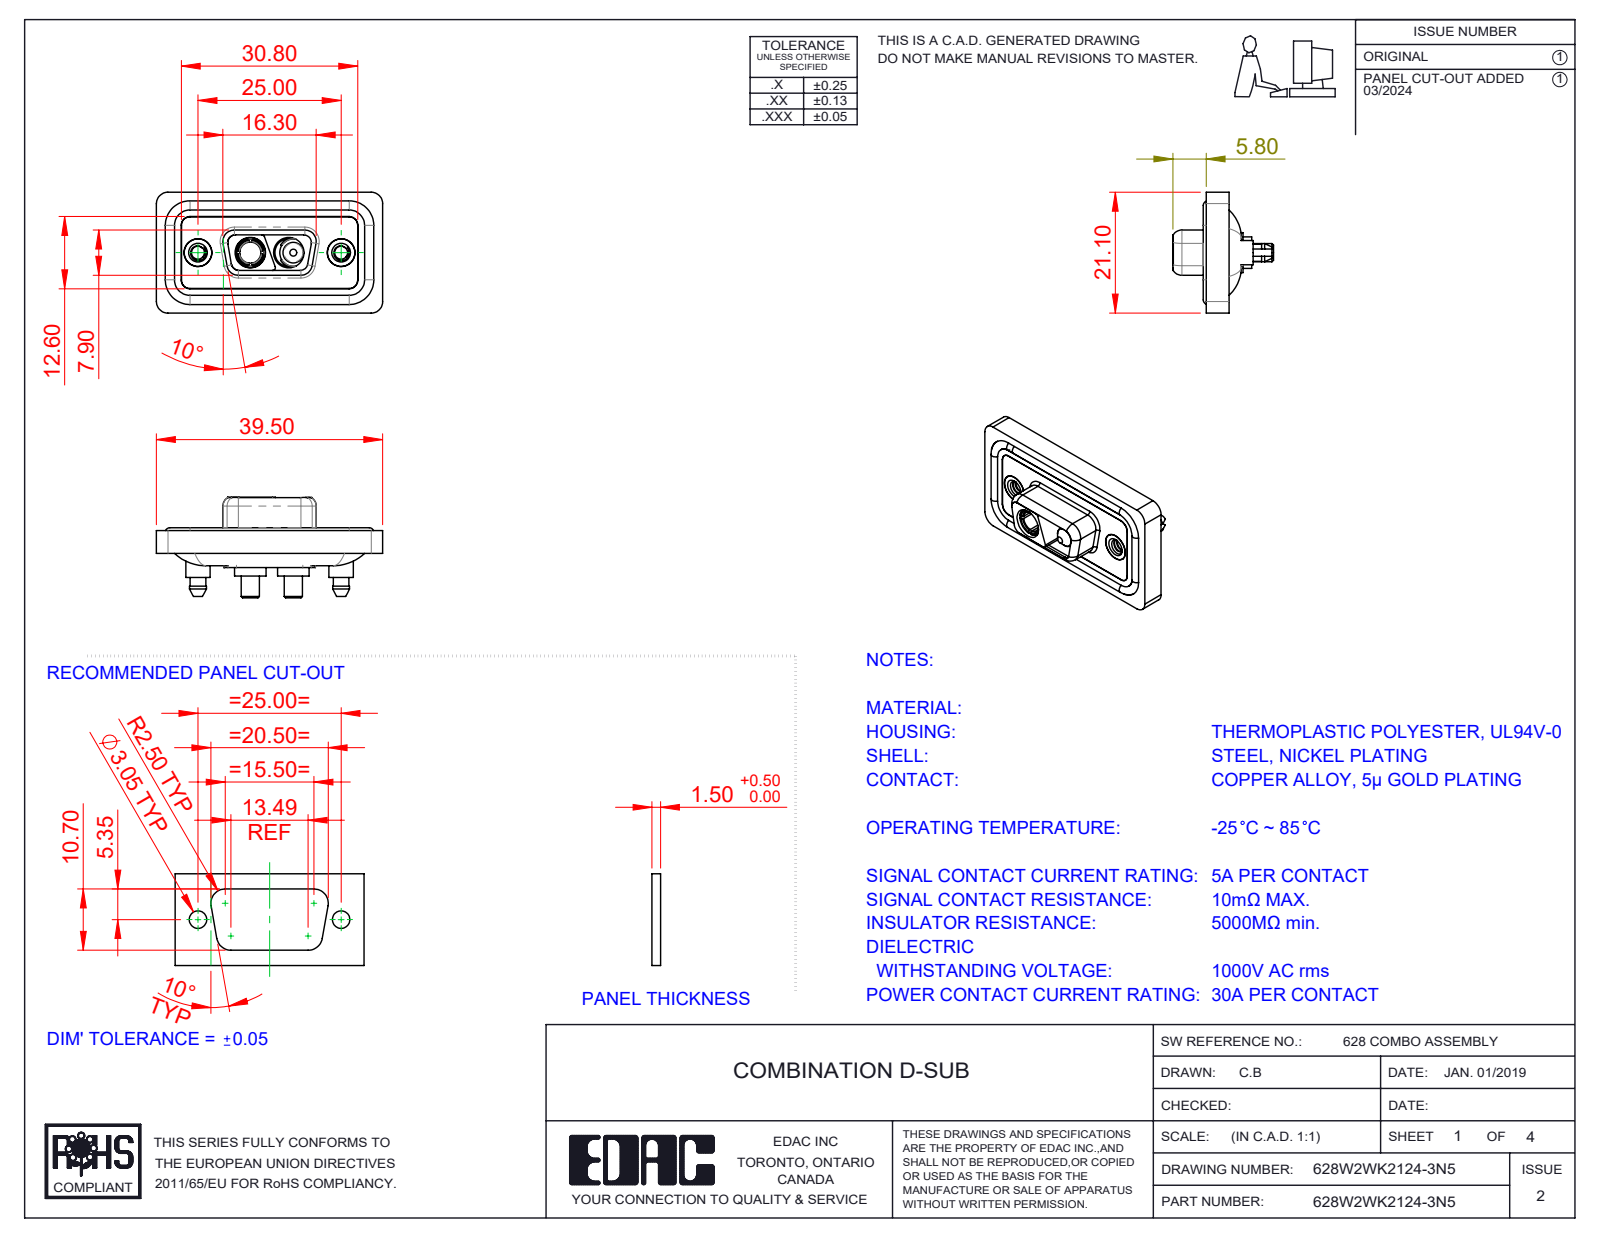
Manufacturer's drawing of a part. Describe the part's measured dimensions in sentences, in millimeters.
The part is named "Power Socket_30A S; 628Combo Shell Rear_09 Contacts; 628Combo Threaded Boardlock_5; Power Pin_30A S (+4 more)". Its 3-D file was written by "SolidWorks 2023 (CONFIG_CONTROL_DESIGN)". It is 11 solids with 550 faces: 160 planar, 263 cylindrical and 127 other. Overall it measures 39.5 by 21.1 by 17.55 millimeters. Its volume is 4 751 cubic millimeters and its surface area 7 686 square millimeters. Round holes: 4 of diameter 4.85, 2 of diameter 2.26, 2 of diameter 4, 2 of diameter 4.05, 2 of diameter 5, 2 of diameter 5.3, 1 of diameter 3.7. Round bosses or shafts: 4 of diameter 1.6, 2 of diameter 5.5, 2 of diameter 5.4, 2 of diameter 5.2, 2 of diameter 4.95, 2 of diameter 4.8, 2 of diameter 4.75, 2 of diameter 4.25. Partial cylindrical surfaces (rounded edges, fillets, slot ends): 24 of radius 1.5, 18 of radius 2, 10 of radius 1.6, 8 of radius 1.35, 6 of radius 0.5, 4 of radius 0.25, 4 of radius 0.6, 4 of radius 0.65. The main face-to-face distances are 0.4, 1.1, 2.9, 1.6, 0.5, 1.8, 5.65, 1.5, 4, 5.35. The hole center spacings are 9.14, 15.86, 6.72, 25.
